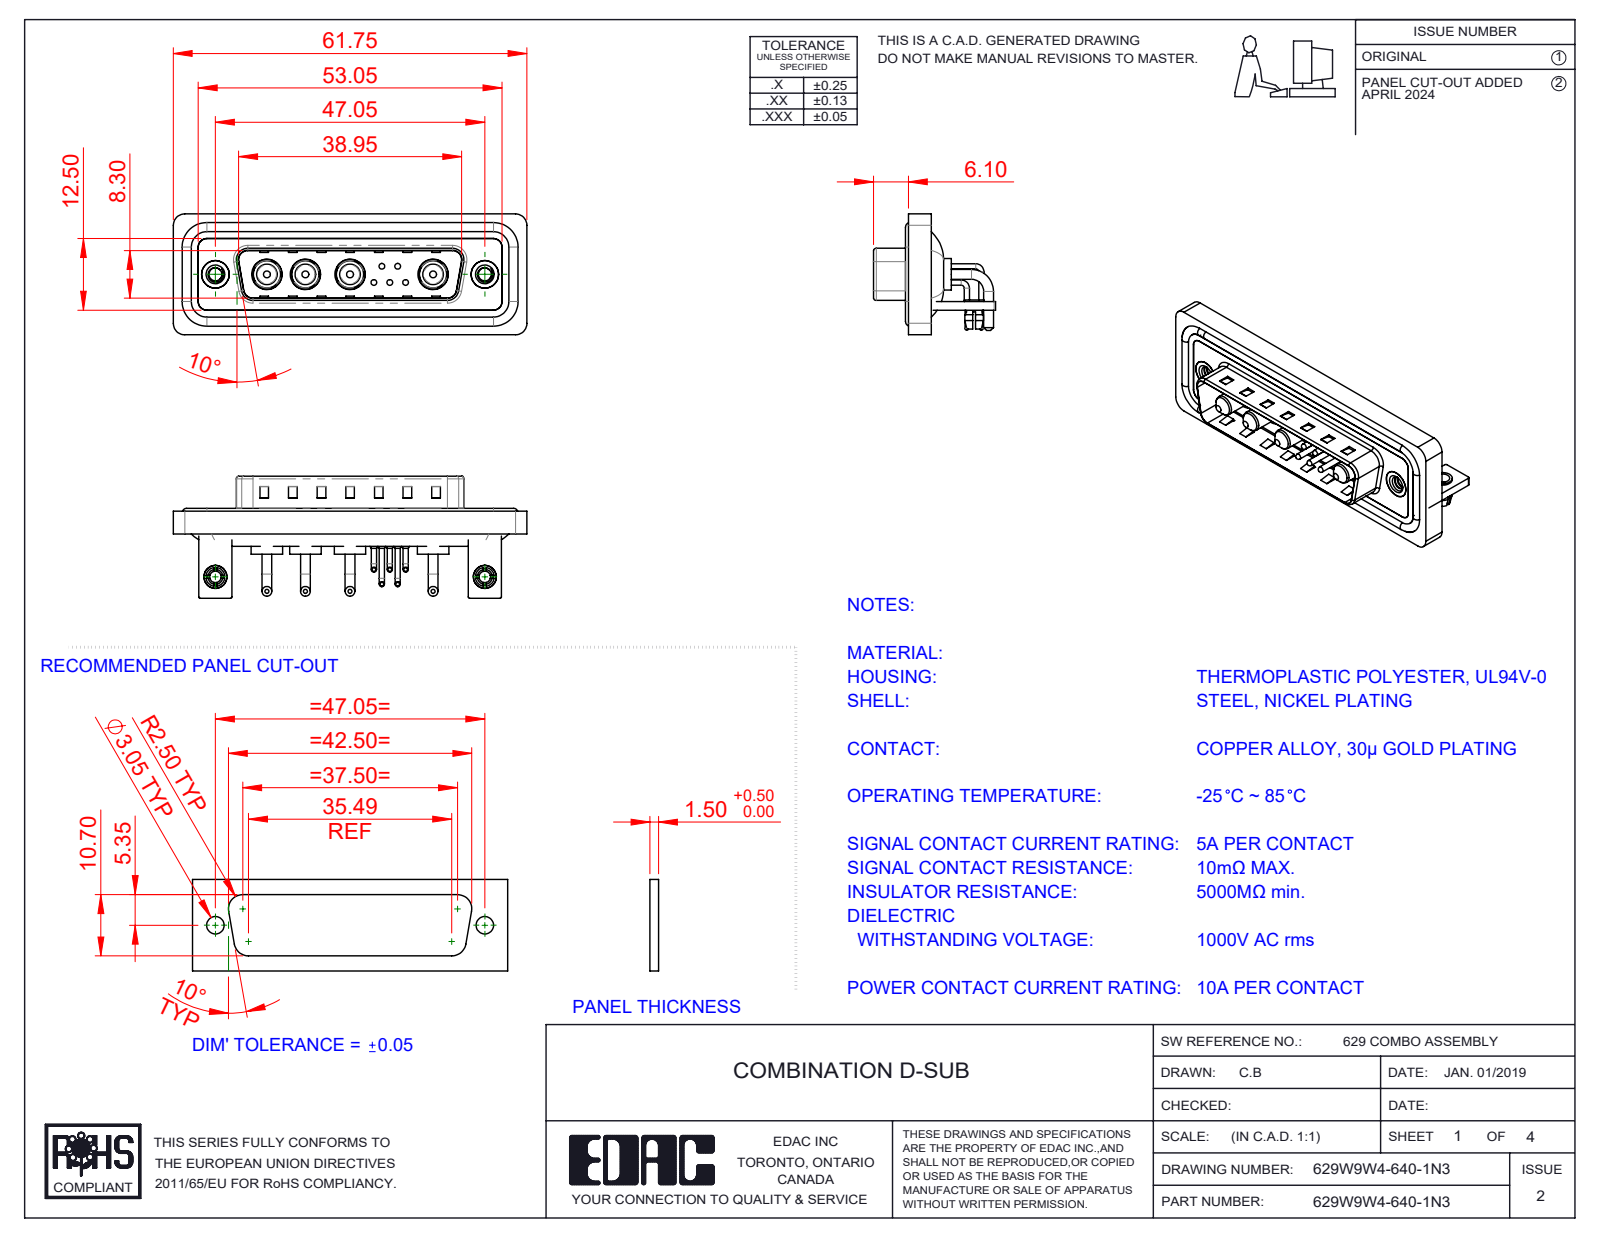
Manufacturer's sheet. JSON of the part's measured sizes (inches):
{"part_name": "Power Pin_10A RA; 629Combo Housing_9W4; 629Combo Stabilizer Bracket; 629W9W4-640-1N3 (+7 more)", "step_written_by": "SolidWorks 2023 (CONFIG_CONTROL_DESIGN)", "units": "inches", "bodies": {"solids": 24, "faces": 1337, "planar": 637, "cylindrical": 502, "other": 198}, "overall_size": [2.431, 0.839, 0.831], "volume_in3": 0.475, "surface_area_in2": 20.1, "round_holes": [[0.079, 7], [0.03, 5], [0.063, 5], [0.191, 4], [0.209, 4], [0.089, 2], [0.098, 2], [0.126, 2], [0.157, 2], [0.189, 2], [0.197, 2]], "round_bosses_or_shafts": [[0.035, 10], [0.067, 8], [0.059, 5], [0.039, 5], [0.026, 5], [0.217, 4], [0.205, 4], [0.187, 4]], "partial_cylinders_radius": [[0.079, 19], [0.059, 18], [0.01, 16], [0.02, 9], [0.063, 8], [0.04, 5], [0.024, 4], [0.026, 4]], "face_to_face_distances": [0.016, 0.059, 0.031, 0.114, 0.083, 0.043, 0.146, 0.161, 0.177, 0.063], "hole_center_spacings": [0.124, 0.109, 0.198, 0.571, 1.852, 0.109, 0.173, 0.174]}
